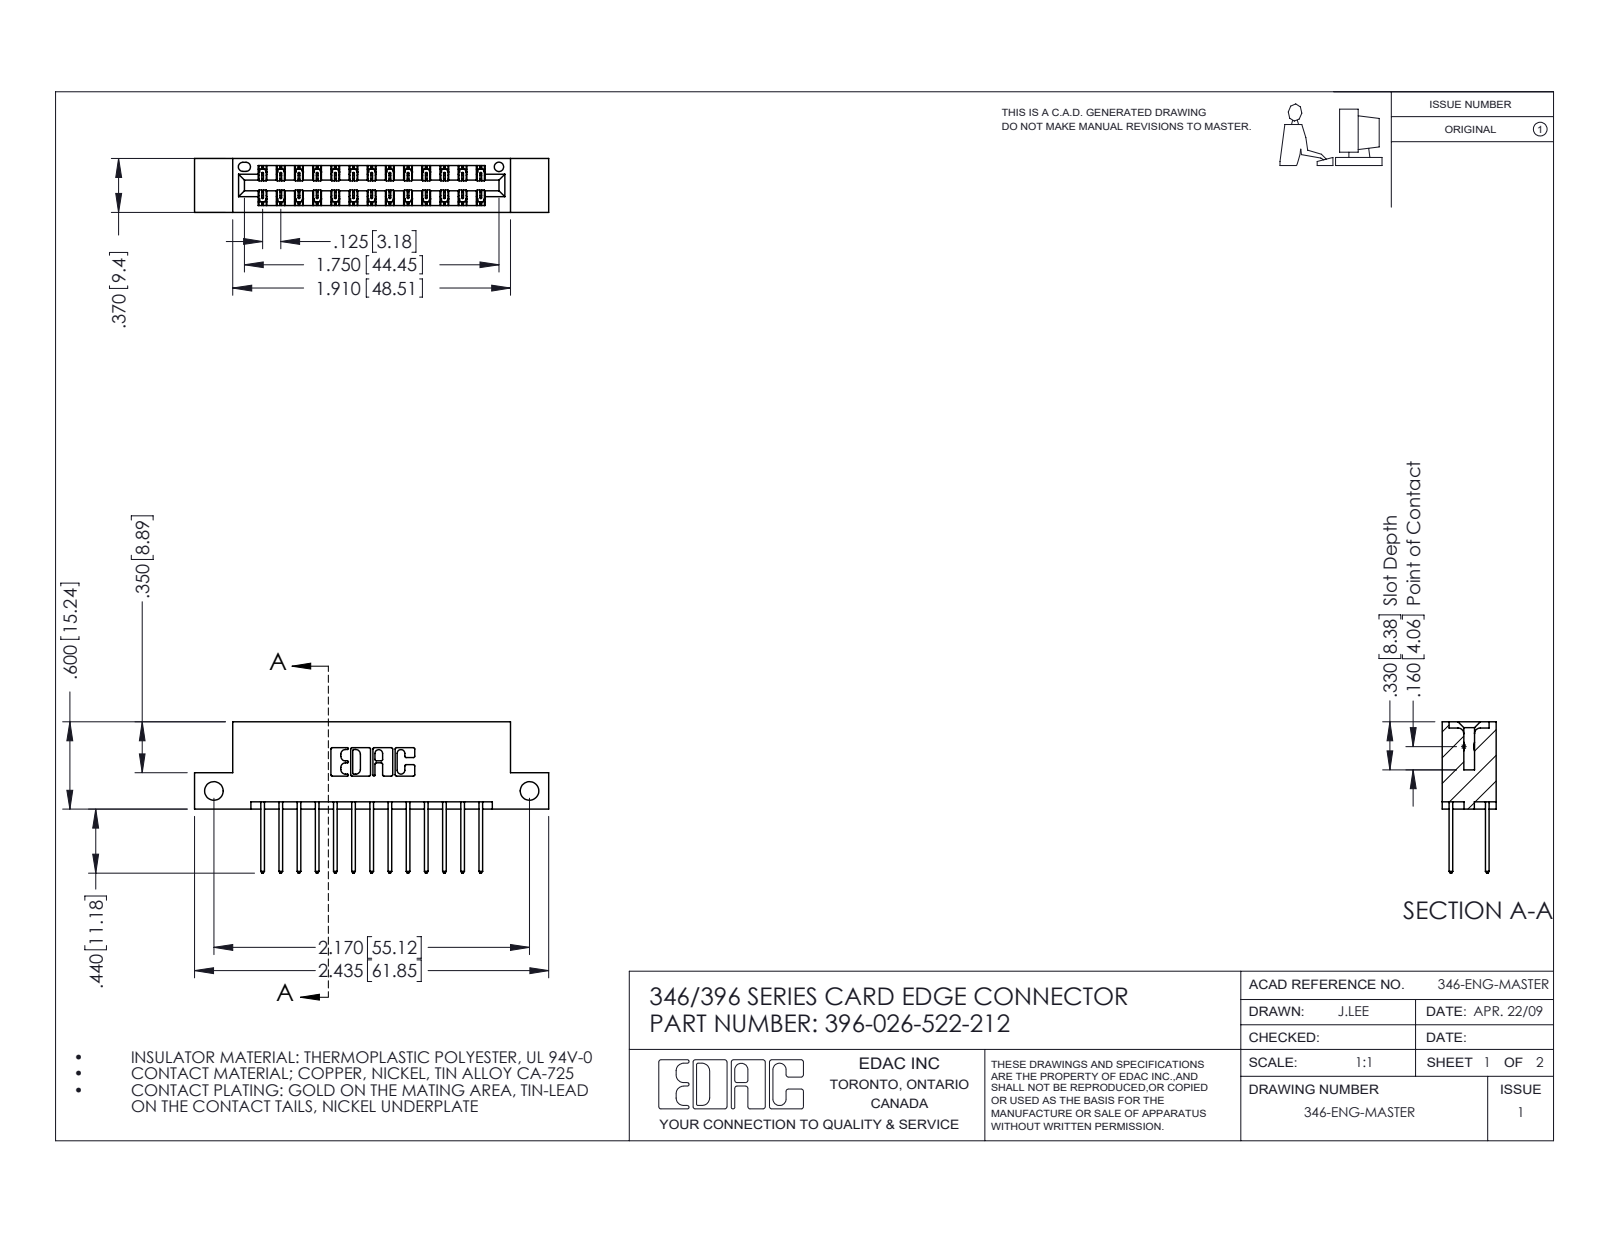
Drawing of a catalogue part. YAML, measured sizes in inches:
part_name: "345-292-001_345-293-122; 396-026-522-212; 346 Part_Flush Mounting Lugs - Side Mount"
step_written_by: "SolidWorks 2016 (CONFIG_CONTROL_DESIGN)"
units: inches
bodies: {solids: 27, faces: 1474, planar: 986, cylindrical: 488, other: 0}
overall_size: [2.435, 1.04, 0.37]
volume: 0.353
surface_area: 11.88
round_holes:
  - {diameter: 0.128, count: 2}
  - {diameter: 0.064, count: 1}
partial_cylinders:
  - {radius: 0.006, count: 39}
  - {radius: 0.01, count: 26}
  - {radius: 0.01, count: 22}
  - {radius: 0.007, count: 6}
  - {radius: 0.031, count: 6}
  - {radius: 0.026, count: 3}
  - {radius: 0.014, count: 2}
  - {radius: 0.022, count: 2}
face_to_face_distances: [0.25, 0.048, 0.322, 0.37, 0.072, 0.298, 0.025, 0.275, 0.148, 0.222]
hole_center_spacings: [2.17]
